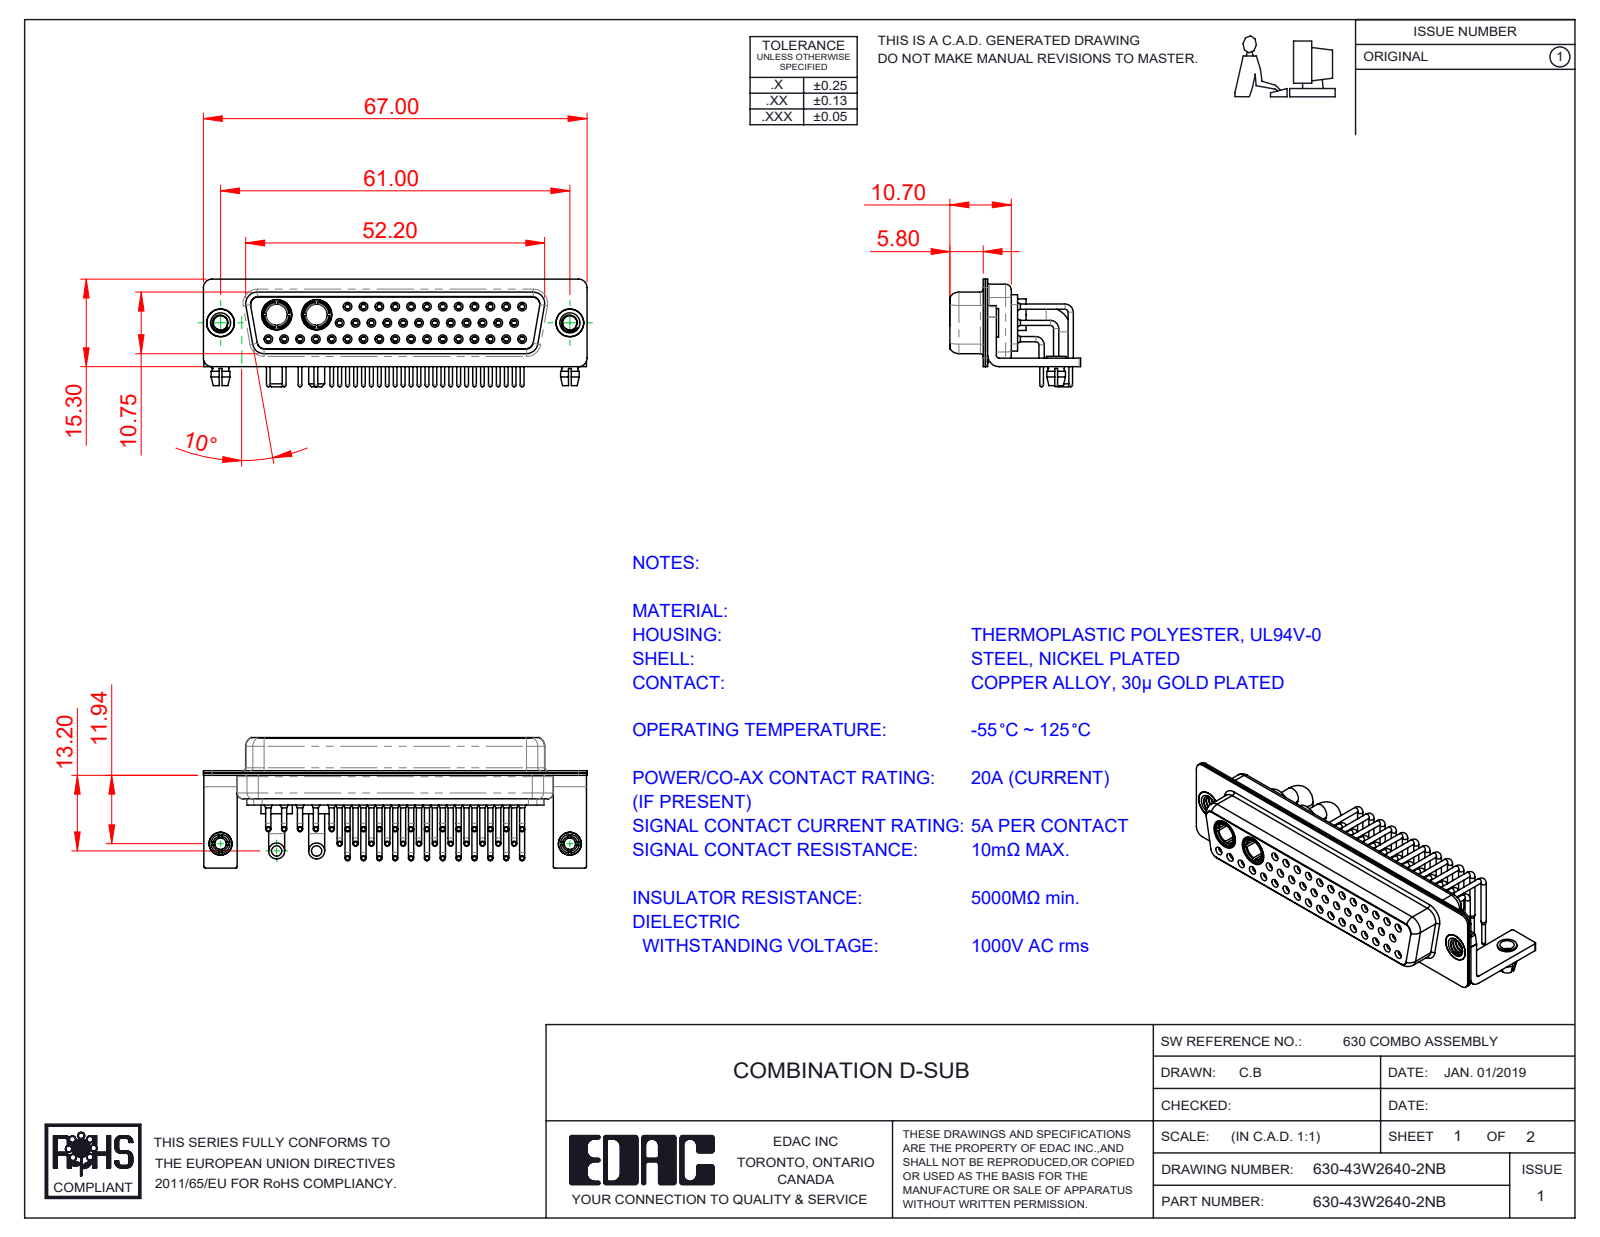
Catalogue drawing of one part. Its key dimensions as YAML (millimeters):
part_name: "630Combo Threaded Rivet_B; 630Combo Housing_43W2; 630-43W2640-2NB; 630Combo Stabilizer Bracket_50 Contacts (+7 more)"
step_written_by: "SolidWorks 2020 (CONFIG_CONTROL_DESIGN)"
units: millimeters
bodies: {solids: 54, faces: 2738, planar: 808, cylindrical: 1180, other: 750}
overall_size: [67, 22.8, 18.8]
volume: 7598
surface_area: 16776
round_holes:
  - {diameter: 2, count: 43}
  - {diameter: 0.9, count: 41}
  - {diameter: 1.1, count: 41}
  - {diameter: 1.5, count: 41}
  - {diameter: 1.6, count: 29}
  - {diameter: 1.7, count: 12}
  - {diameter: 2.5, count: 4}
  - {diameter: 4.85, count: 4}
  - {diameter: 3.2, count: 2}
  - {diameter: 3.7, count: 2}
  - {diameter: 4, count: 2}
  - {diameter: 4.05, count: 2}
round_bosses_or_shafts:
  - {diameter: 0.9, count: 41}
  - {diameter: 0.65, count: 41}
  - {diameter: 1.6, count: 12}
  - {diameter: 2.8, count: 4}
  - {diameter: 5.5, count: 2}
  - {diameter: 5.2, count: 2}
  - {diameter: 5, count: 2}
  - {diameter: 4.96, count: 2}
partial_cylinders:
  - {radius: 0.25, count: 16}
  - {radius: 1.5, count: 16}
  - {radius: 2, count: 13}
  - {radius: 1.35, count: 12}
  - {radius: 1.6, count: 8}
  - {radius: 0.5, count: 5}
  - {radius: 0.6, count: 4}
  - {radius: 0.65, count: 4}
face_to_face_distances: [0.4, 1.5, 6, 5.6, 0.8, 5.8, 5.2, 11.28, 1.82, 10.35]
hole_center_spacings: [2.77, 3.16, 5.54, 8.31, 11.08, 13.85, 16.62, 19.39]
